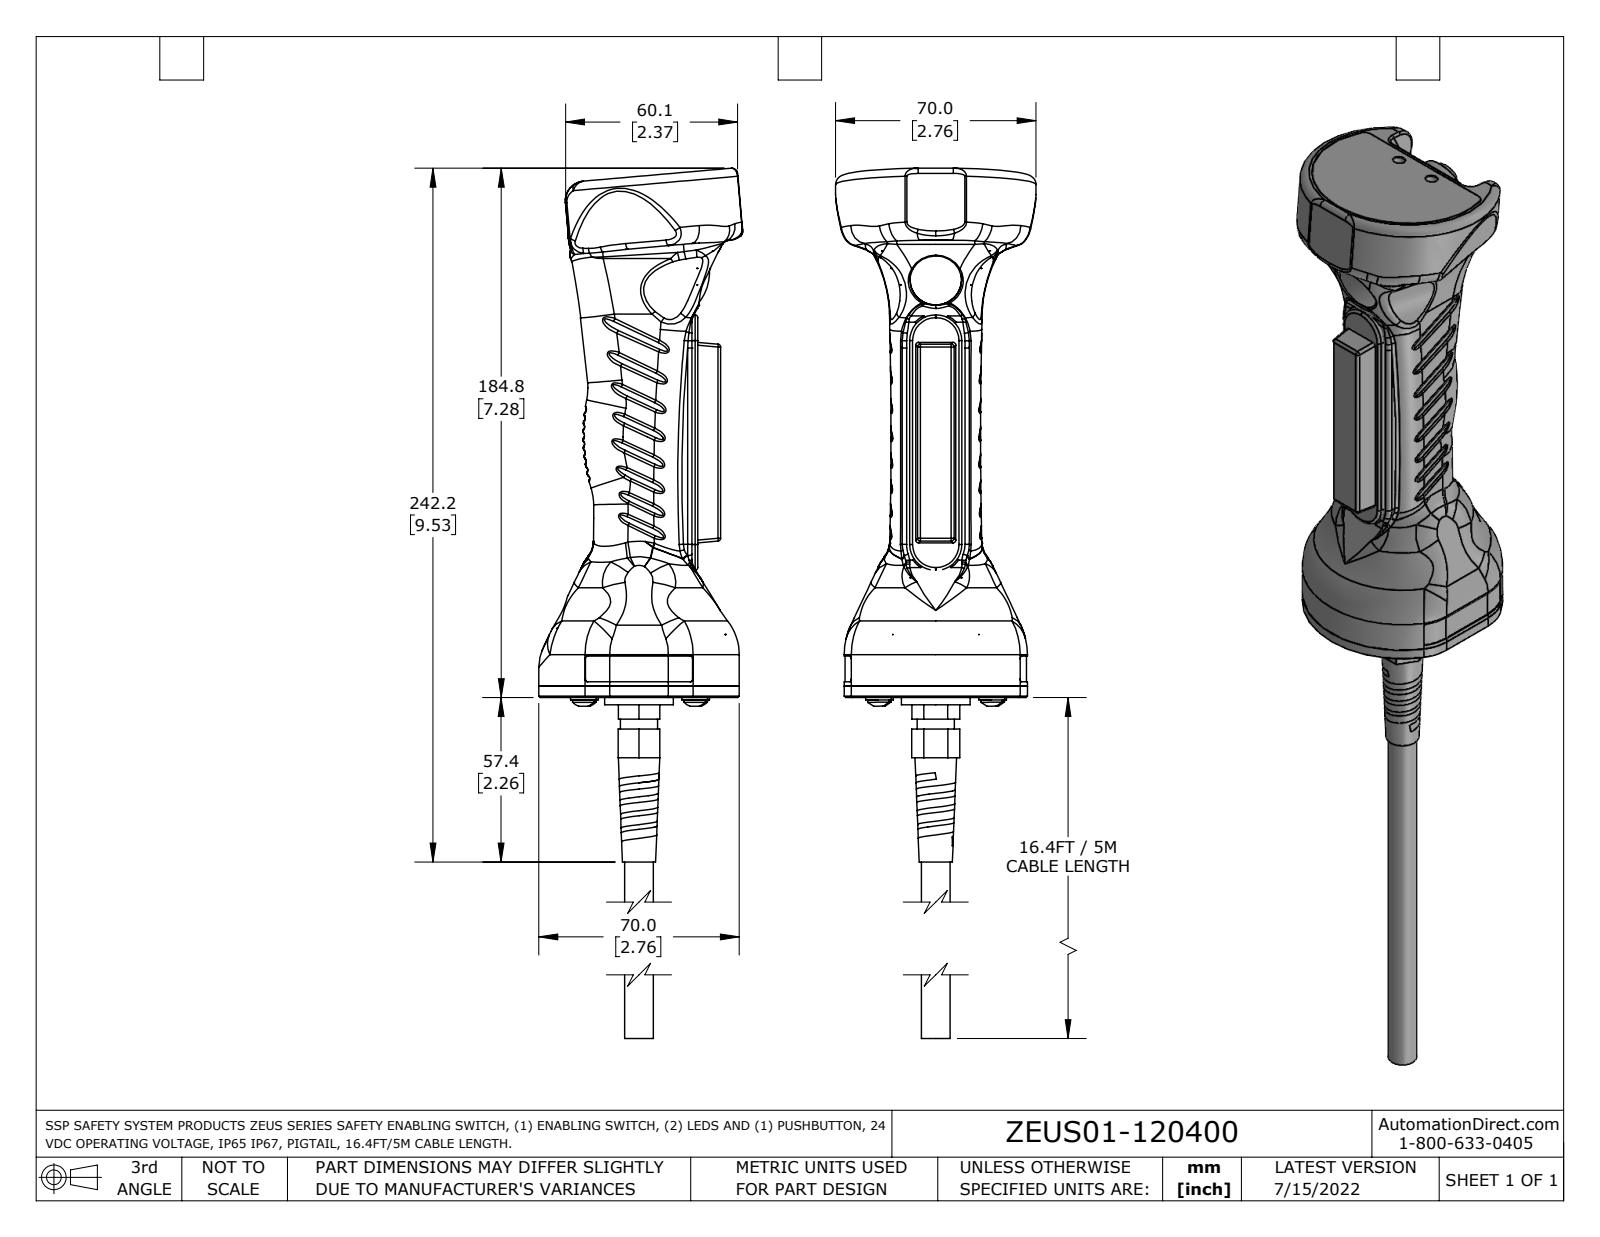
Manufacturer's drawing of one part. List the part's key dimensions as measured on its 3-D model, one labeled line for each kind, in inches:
Part name (STEP PRODUCT): ZEUS01-120400
STEP written by: SolidWorks 2021 (AUTOMOTIVE_DESIGN)
Units: inches
Bodies: 18 solids, 1376 faces (470 planar, 455 cylindrical, 451 other)
Overall size (bounding box): 14.926 × 2.803 × 2.756
Volume: 23.81 in³ · Surface area: 129.3 in²
Round holes (diameter × count): ⌀0.132 ×4, ⌀0.169 ×4, ⌀0.177 ×4, ⌀0.197 ×4, ⌀0.098 ×2, ⌀0.11 ×2, ⌀0.165 ×2, ⌀0.173 ×2, ⌀0.331 ×2, ⌀0.039 ×1, ⌀0.159 ×1, ⌀0.201 ×1
Round bosses / shafts (diameter × count): ⌀0.354 ×4, ⌀0.295 ×4, ⌀0.157 ×4, ⌀0.039 ×4, ⌀0.461 ×2, ⌀0.236 ×2, ⌀0.945 ×1, ⌀0.827 ×1
Partial cylindrical surfaces — rounded edges, fillets, slot ends (radius × count): R0.005 ×96, R0.039 ×51, R0.028 ×48, R0.079 ×21, R0.008 ×20, R0.118 ×10, R0.006 ×8, R0.031 ×7
Main face-to-face distances: 0.157, 0.079, 0.014, 0.02, 0.065, 0.059, 0.098, 0.177, 0.039, 0.571
Hole centre spacings: 1.531, 0.63, 1.181, 1.558, 2.184, 0.404, 0.404, 0.513
